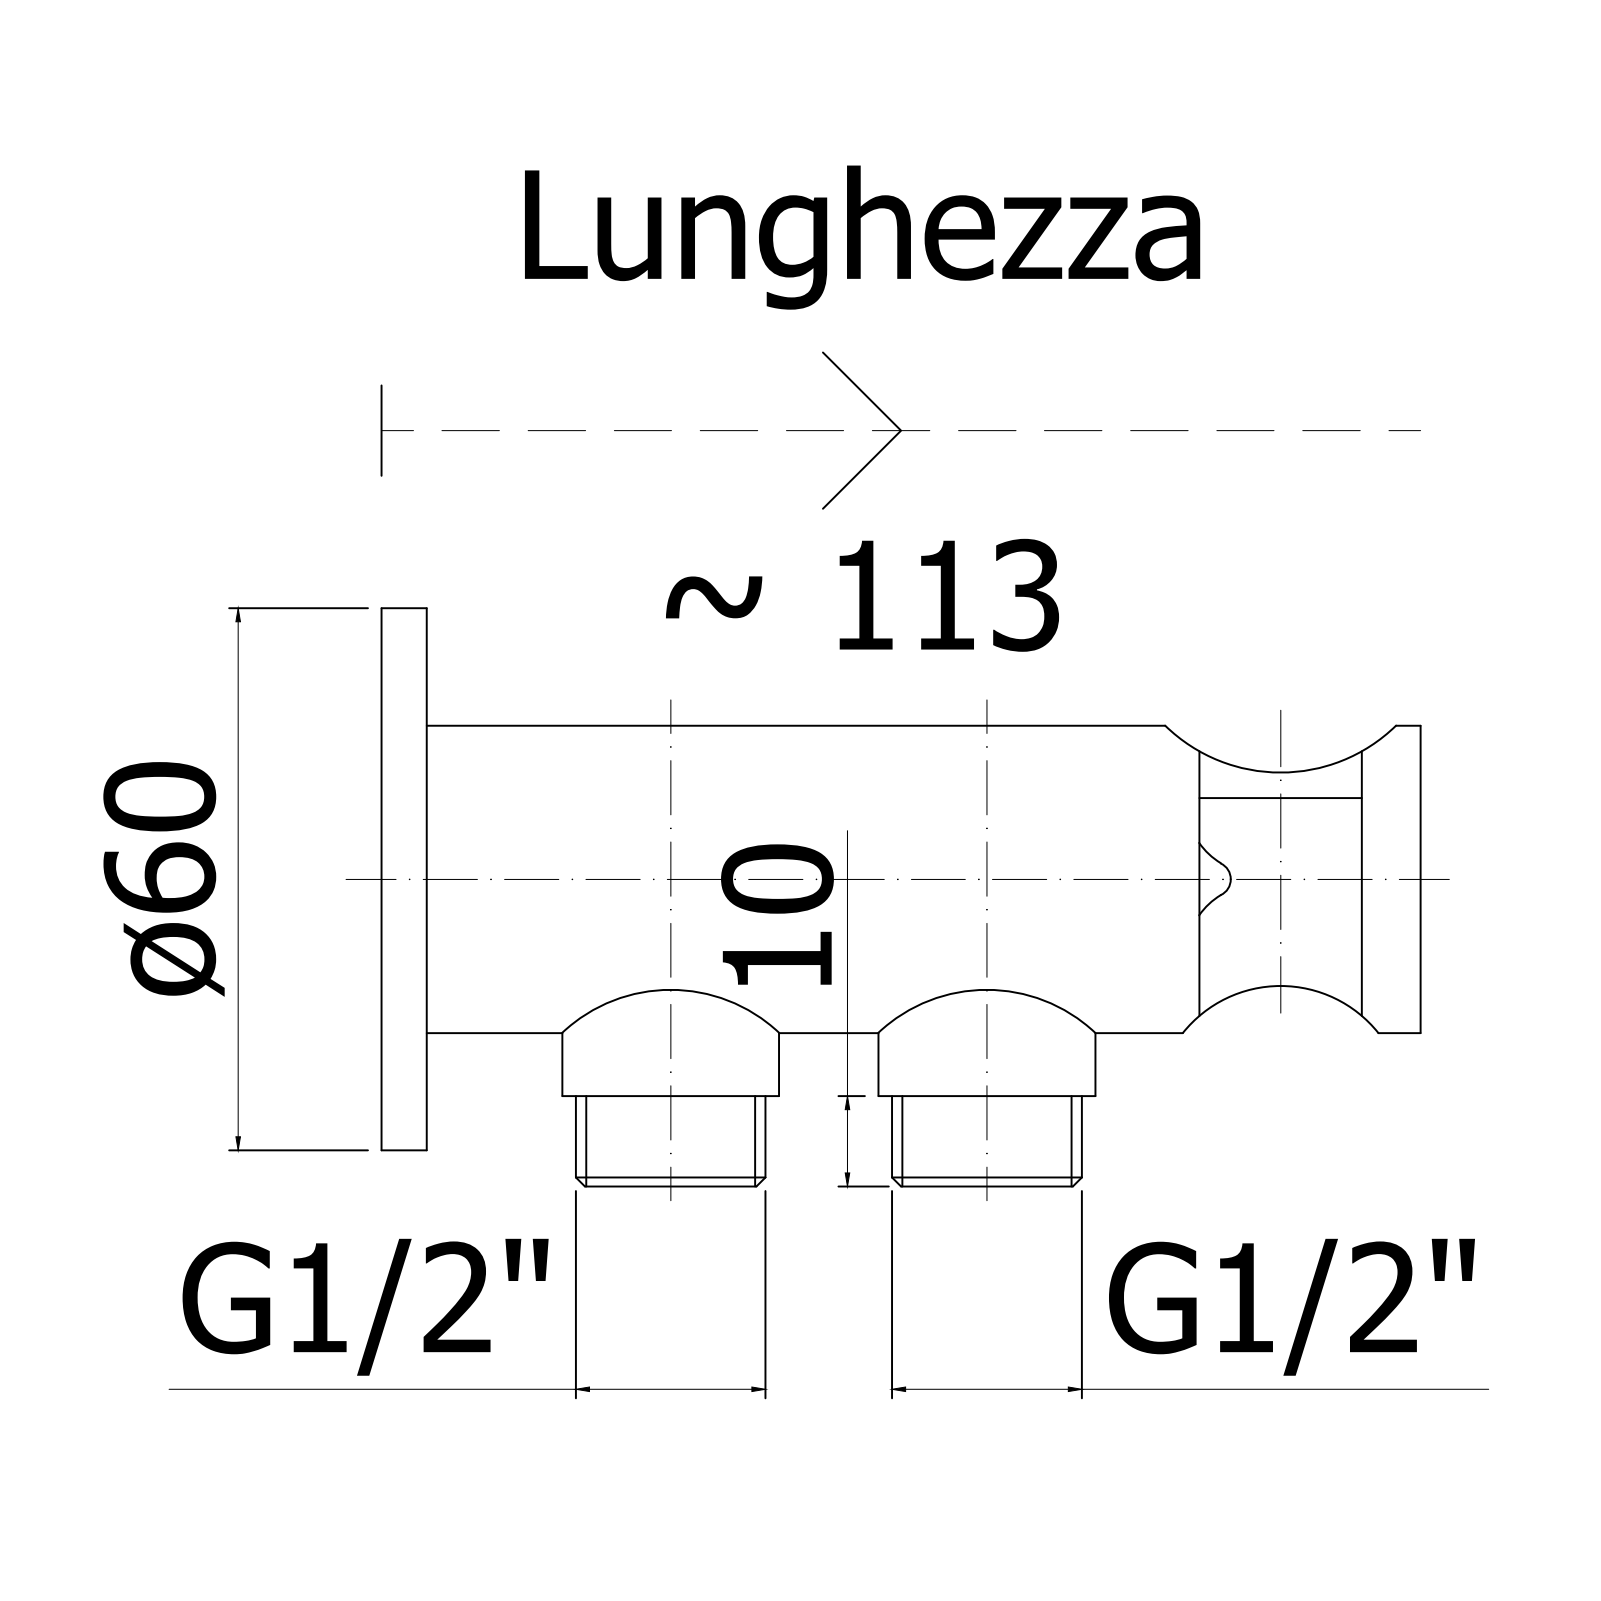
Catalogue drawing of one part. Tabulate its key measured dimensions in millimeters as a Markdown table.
| quantity | value |
| --- | --- |
| part name | ZSUP028CR |
| STEP written by | CREO PARAMETRIC BY PTC INC, 2020044 (CONFIG_CONTROL_DESIGN) |
| units | millimeters |
| bodies | 2 solids, 164 faces (69 planar, 72 cylindrical, 23 other) |
| overall size | 113.1 × 62.75 × 60 |
| volume | 88 100 mm³ |
| surface area | 28 962 mm² |
| round holes (diameter × count) | 15 × 3, 6.5 × 2, 3.3 × 1, 5.5 × 1, 8.5 × 1, 18.5 × 1, 19.5 × 1, 21.5 × 1, 23 × 1, 34 × 1, 38 × 1, 54 × 1 |
| round bosses / shafts (diameter × count) | 24 × 2, 20.7 × 2, 60 × 1, 41.5 × 1, 31.5 × 1, 21 × 1, 19 × 1, 18.3 × 1 |
| partial cylindrical surfaces (radius × count) | 2.5 × 3 |
| main face-to-face distances | 4.9, 5, 0.8, 4.1, 112.9, 112.1, 108, 4, 1, 0.9 |
| hole center spacings | 33 |
